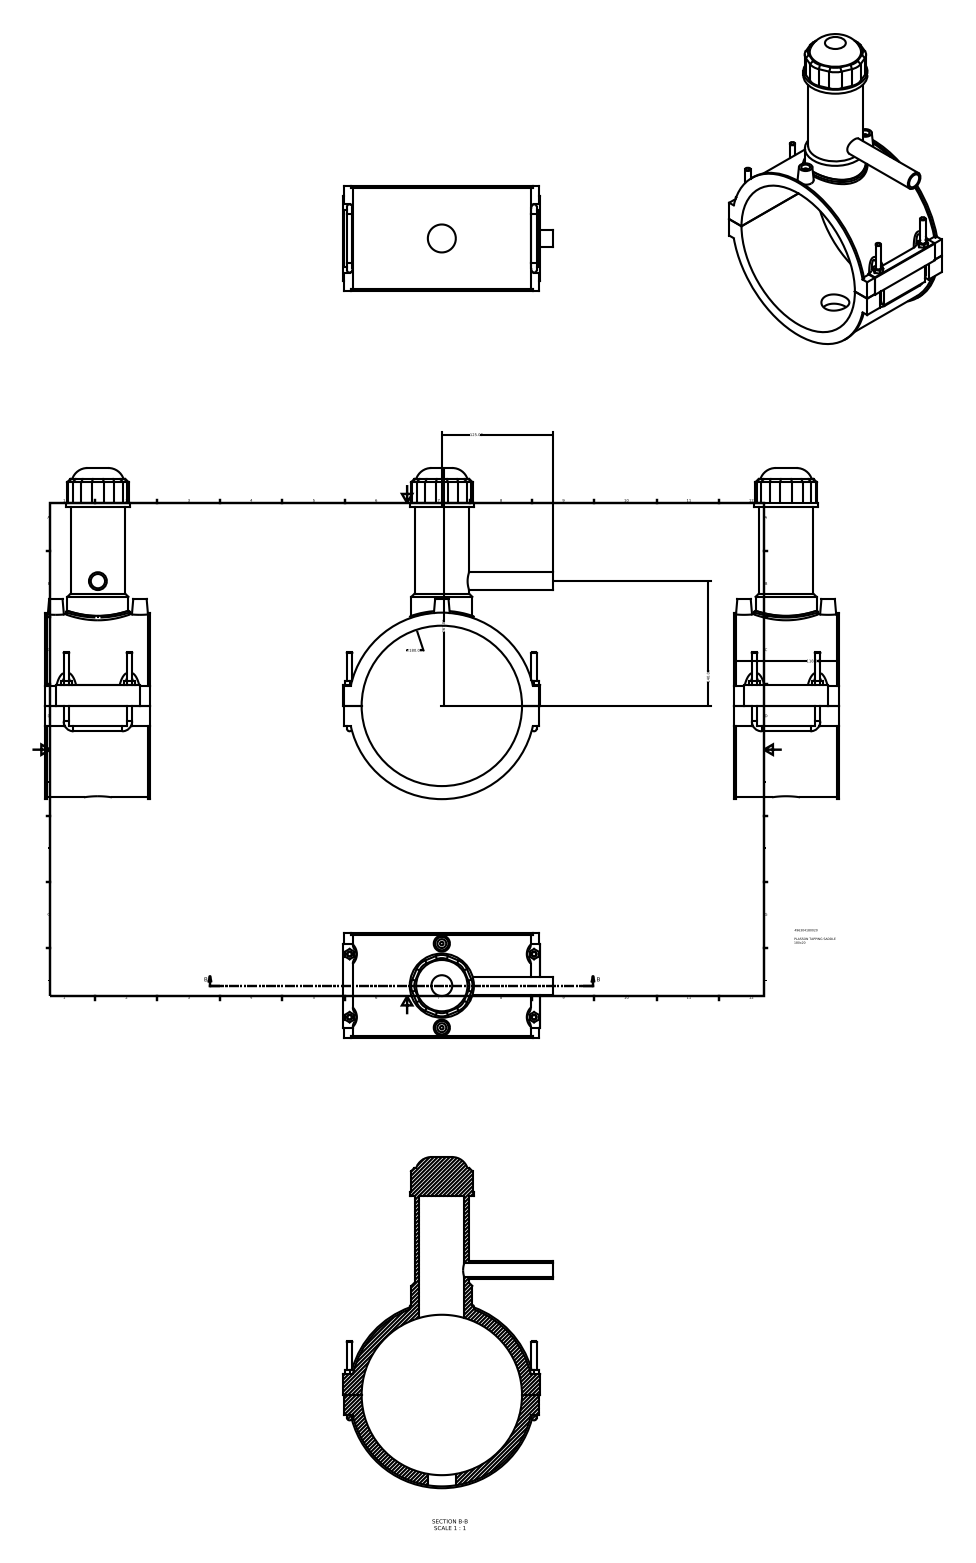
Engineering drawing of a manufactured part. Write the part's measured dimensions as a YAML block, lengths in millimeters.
part_name: "496304180020"
step_written_by: "Autodesk Inventor 2015 (AUTOMOTIVE_DESIGN)"
units: millimeters
bodies: {solids: 1, faces: 184, planar: 110, cylindrical: 49, other: 25}
overall_size: [371.65, 235.5, 118]
volume: 1254000
surface_area: 253751
round_holes:
  - {diameter: 10, count: 2}
  - {diameter: 16, count: 1}
  - {diameter: 31.36, count: 1}
  - {diameter: 50.4, count: 1}
  - {diameter: 180, count: 1}
round_bosses_or_shafts:
  - {diameter: 6, count: 6}
  - {diameter: 4, count: 2}
  - {diameter: 209.3, count: 1}
  - {diameter: 205.2, count: 1}
  - {diameter: 72, count: 1}
  - {diameter: 68.4, count: 1}
  - {diameter: 61.2, count: 1}
  - {diameter: 20, count: 1}
partial_cylinders:
  - {radius: 18, count: 8}
  - {radius: 3, count: 4}
  - {radius: 7.5, count: 4}
  - {radius: 0.5, count: 1}
  - {radius: 106.7, count: 1}
face_to_face_distances: [118, 1, 220, 222.8, 222.7, 219, 22.45, 22.55, 2.36, 115.64]
hole_center_spacings: [47.2, 94.4]
